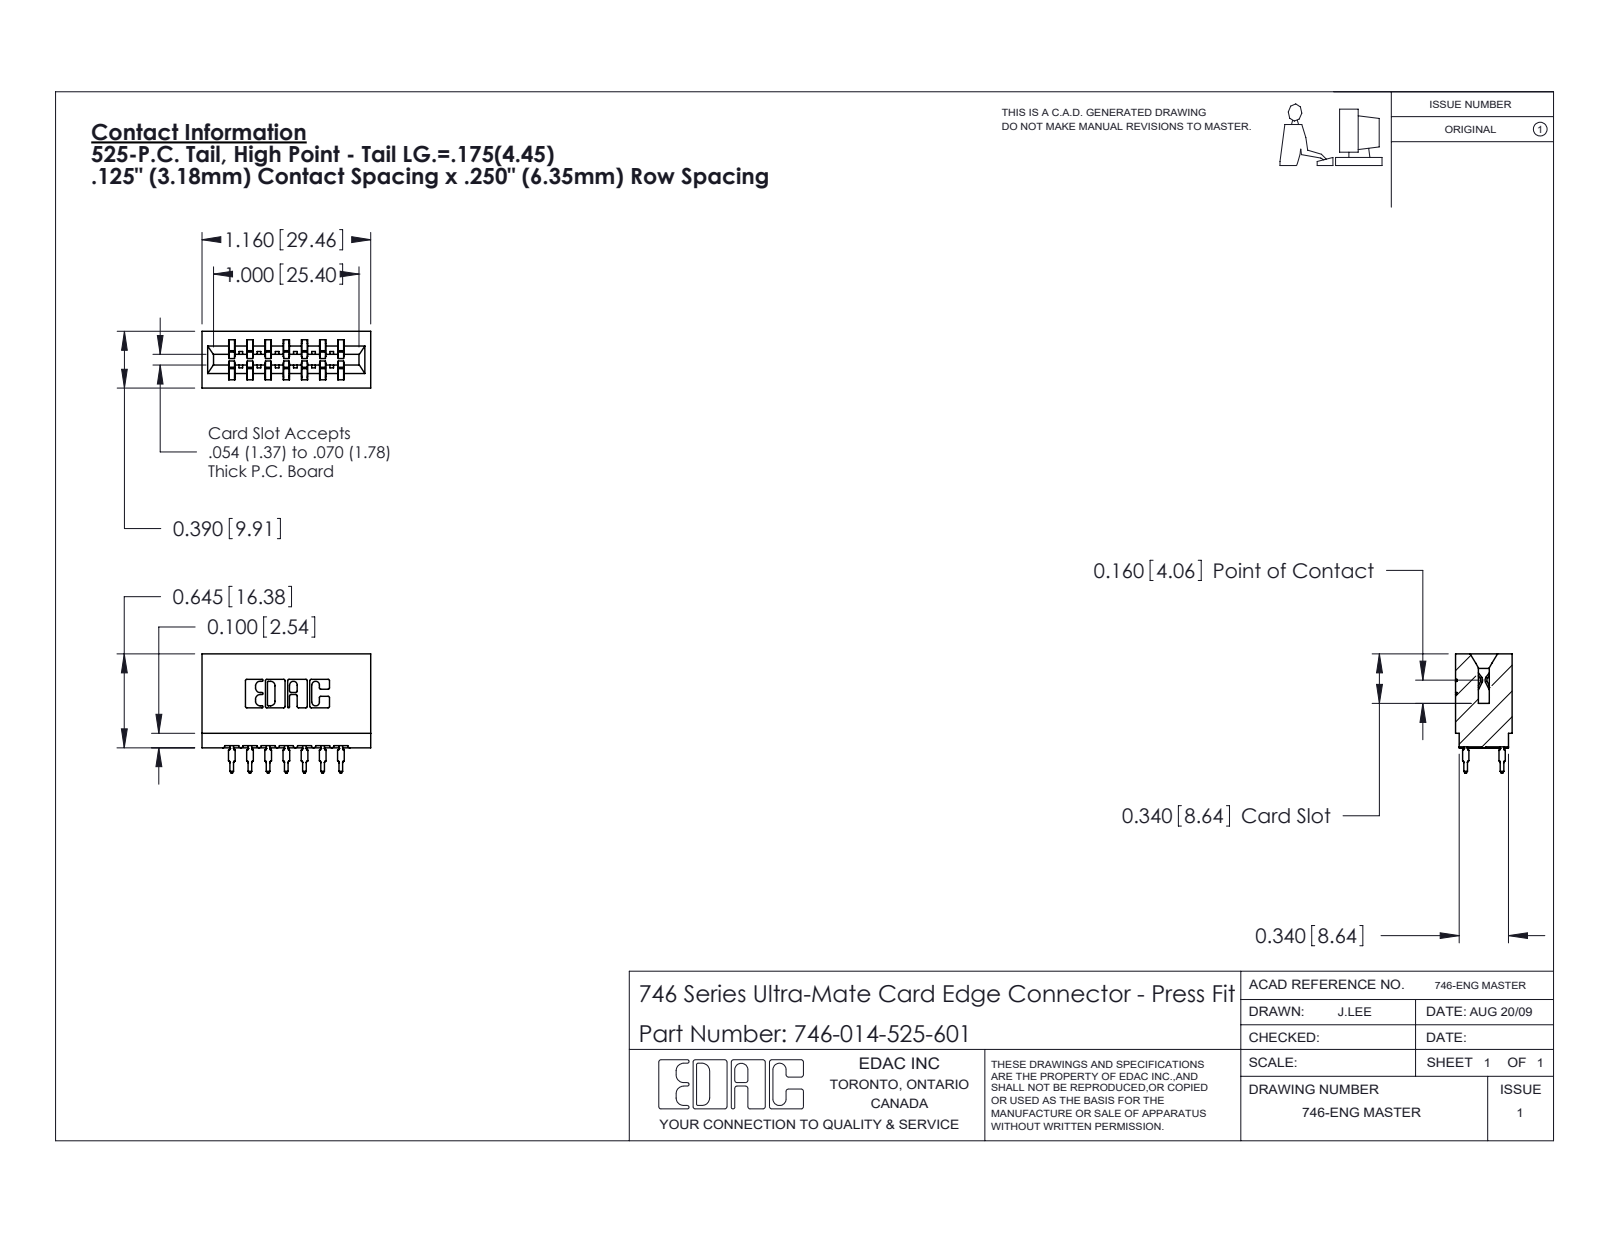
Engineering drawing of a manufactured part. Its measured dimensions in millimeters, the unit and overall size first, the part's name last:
Units: millimetres
Overall size (bounding box): 29.5 × 20.8 × 9.9
Partial cylindrical surfaces — rounded edges, fillets, slot ends (radius × count): R0.5 ×28, R0.3 ×22, R0.1 ×8, R0.3 ×8, R0.4 ×8, R0.2 ×6, R0.8 ×6, R0.7 ×3
Main face-to-face distances: 6.4, 1.1, 8.5, 1.4, 3.2, 3.2, 12.7, 7.4, 5.3, 9.9
Volume: 3 570 mm³ · Surface area: 4 571 mm²
Bodies: 15 solids, 1350 faces (699 planar, 287 cylindrical, 364 other)
Part name (STEP PRODUCT): 746-014-525-601; 746 Part_.340 Slot Depth - 01; 746-292-001_525
STEP written by: SolidWorks 2020 (CONFIG_CONTROL_DESIGN)
